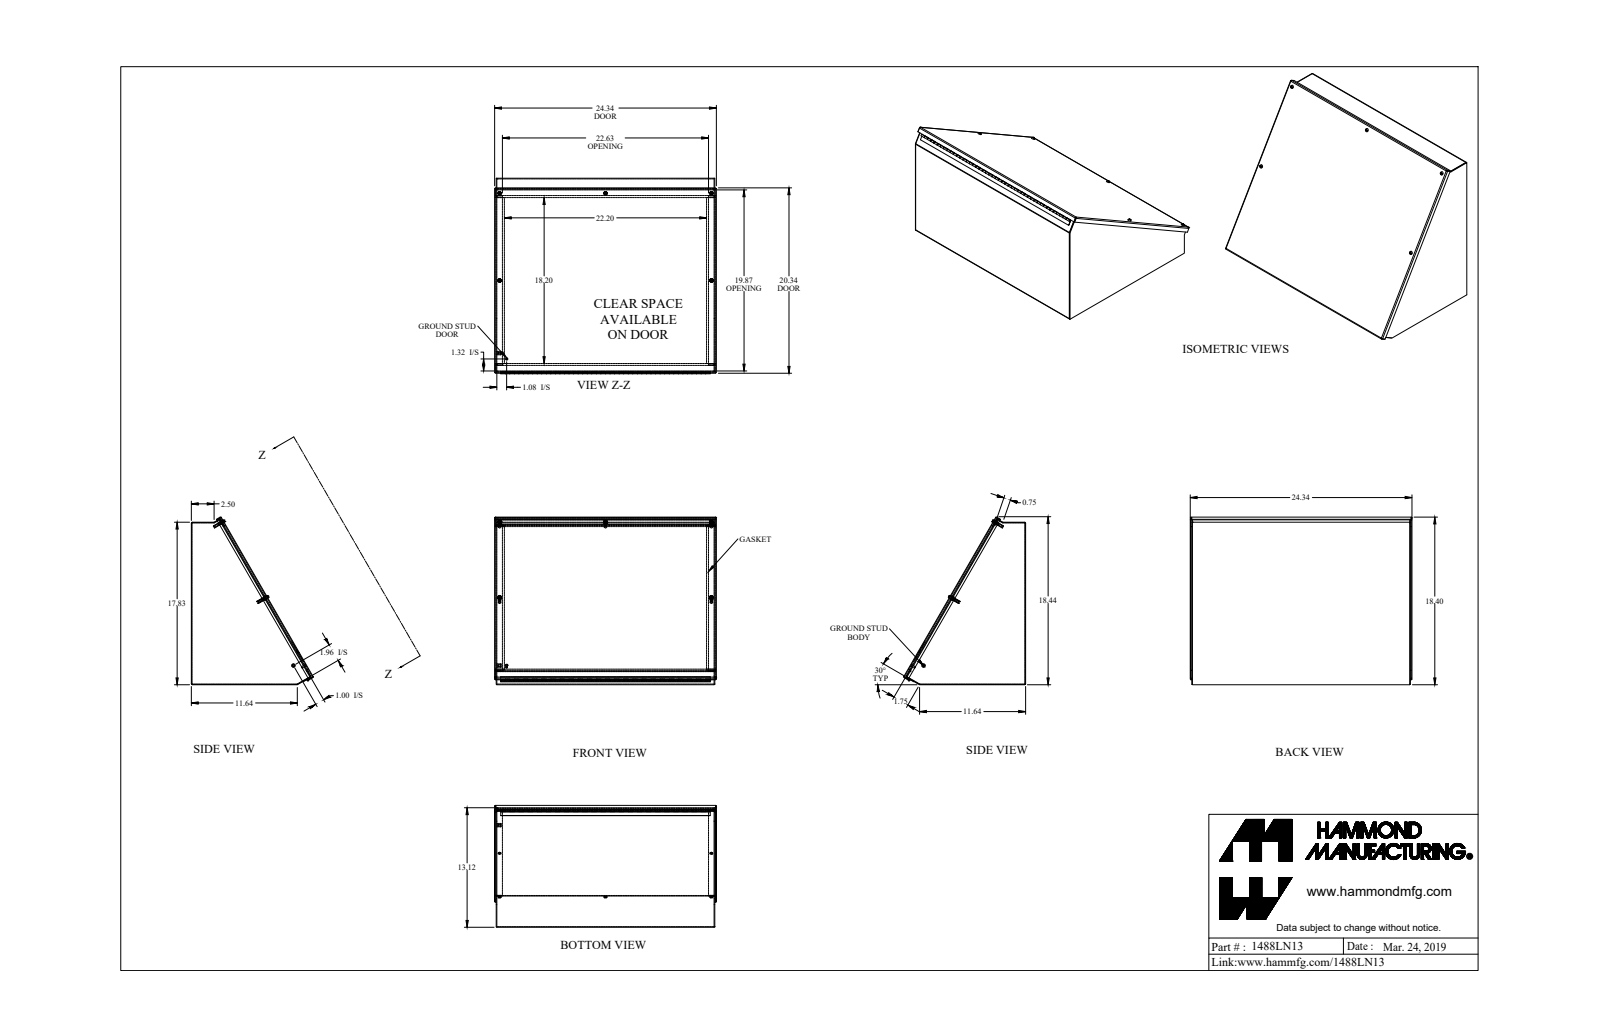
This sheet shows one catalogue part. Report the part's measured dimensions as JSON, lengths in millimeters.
{"part_name": "1488LN13_Default", "step_written_by": "SolidWorks 2019 (CONFIG_CONTROL_DESIGN)", "units": "millimeters", "bodies": {"solids": 26, "faces": 889, "planar": 582, "cylindrical": 259, "other": 48}, "overall_size": [618.3, 467.3, 339.7], "volume_mm3": 2386000, "surface_area_mm2": 2402000, "round_holes": [[4, 5], [6.4, 5], [4, 1]], "round_bosses_or_shafts": [[9.9, 5], [7, 5], [4.8, 5], [3.8, 5], [9.5, 1], [6.4, 1], [4.8, 1], [4.4, 1]], "partial_cylinders_radius": [[0.9, 12], [2.7, 12], [3.2, 5], [4.1, 5], [4.3, 5]], "face_to_face_distances": [1.8, 607.8, 605.9, 609.6, 451.1, 6.4, 5, 3.2, 3.2, 8.2], "hole_center_spacings": [295.3, 590.6, 638.7, 243.3, 243.3, 295.3, 382.6, 590.6]}
